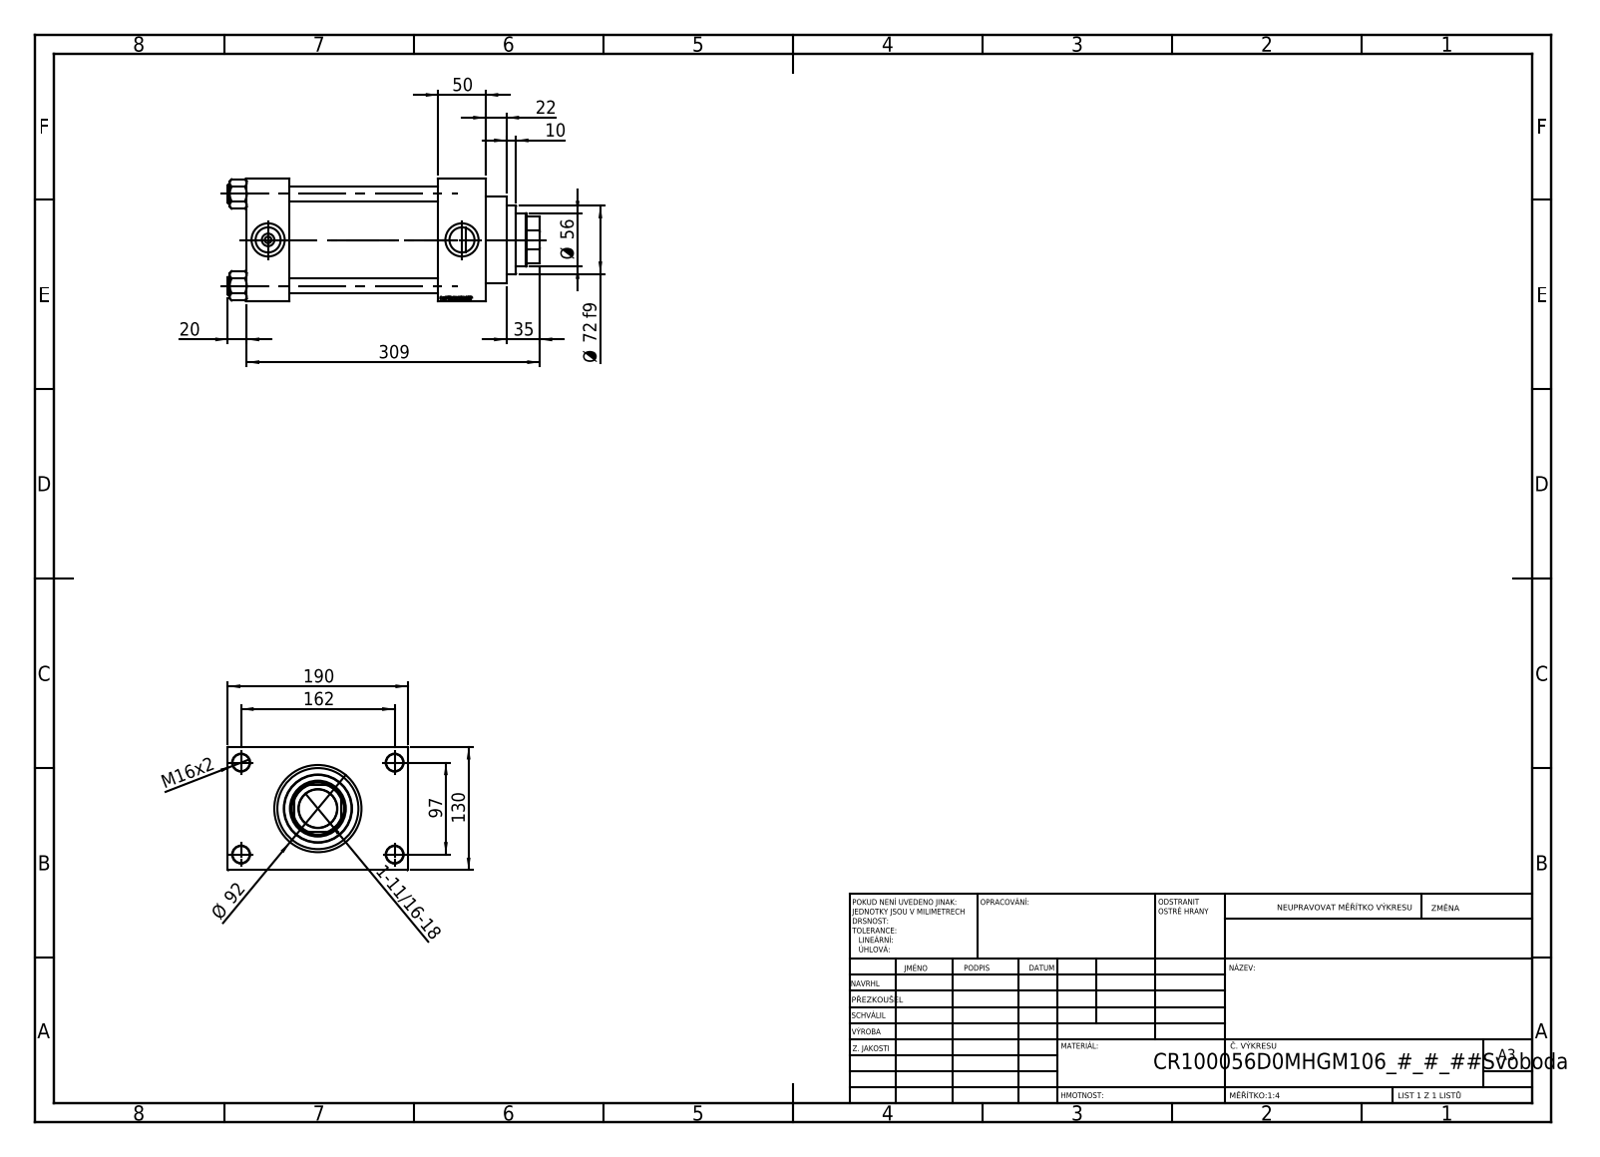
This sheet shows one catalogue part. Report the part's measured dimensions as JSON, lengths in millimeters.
{"part_name": "V215_VC_A; V215CR_VCP_D; NUT_M5_D; V215CR_D_TYCINKA (+1 more)", "step_written_by": "SolidWorks 2019 (CONFIG_CONTROL_DESIGN)", "units": "millimeters", "bodies": {"solids": 11, "faces": 1151, "planar": 545, "cylindrical": 88, "other": 518}, "overall_size": [329, 190, 130], "volume_mm3": 2993000, "surface_area_mm2": 450441, "round_holes": [[16, 4], [18, 4], [7, 2], [26.44, 2], [35, 2], [40.5, 1], [56, 1], [59, 1], [76, 1], [85.5, 1], [100, 1]], "round_bosses_or_shafts": [[19, 4], [106, 1], [92, 1], [72, 1]], "partial_cylinders_radius": [[27, 1]], "face_to_face_distances": [130, 50, 45, 202, 157, 252, 207, 30, 160, 190], "hole_center_spacings": [32.55, 68.52, 94.41, 96.9, 102.27, 129.45, 161.73, 97]}
